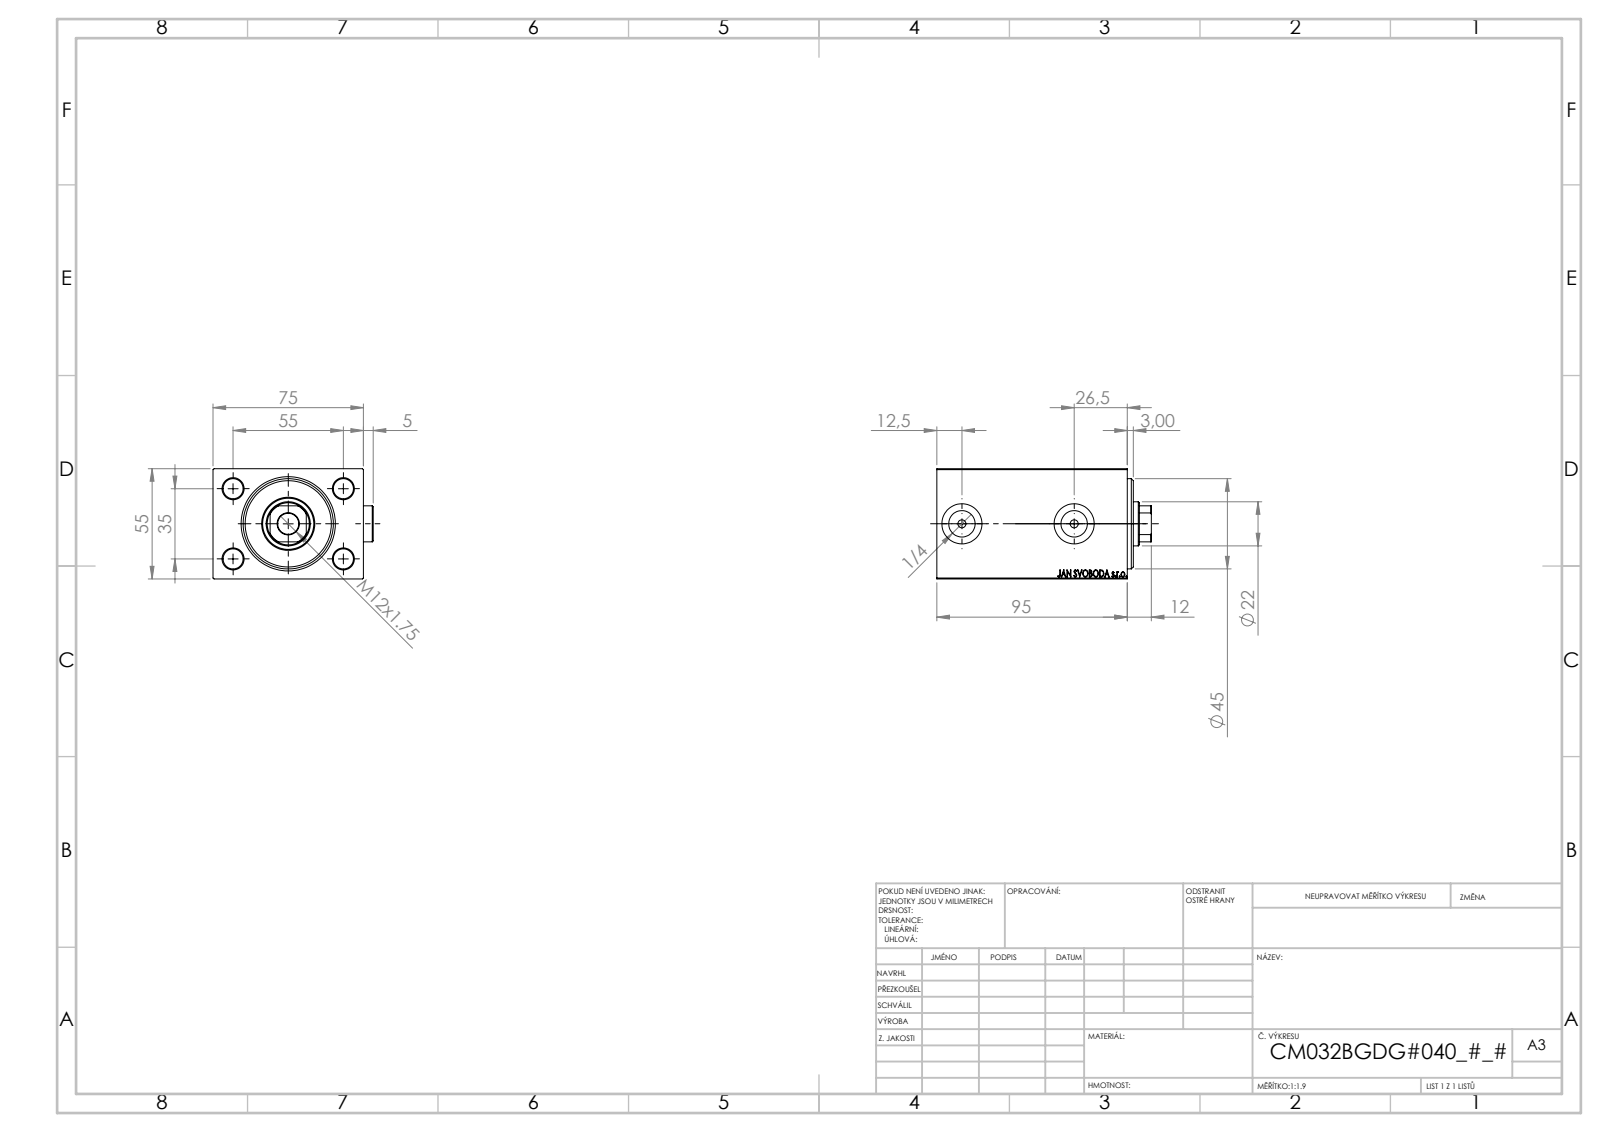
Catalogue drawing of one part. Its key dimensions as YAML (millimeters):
part_name: "Zatka_OIL_PORT; V450CM_VC_B; V450CM_B_Body; V450CM_B_VCP"
step_written_by: "SolidWorks 2019 (CONFIG_CONTROL_DESIGN)"
units: millimeters
bodies: {solids: 5, faces: 935, planar: 435, cylindrical: 70, other: 430}
overall_size: [107, 79.9, 55]
volume: 362108
surface_area: 66059
round_holes:
  - {diameter: 10, count: 4}
  - {diameter: 4, count: 2}
  - {diameter: 13.16, count: 2}
  - {diameter: 20, count: 2}
  - {diameter: 10.5, count: 1}
  - {diameter: 22, count: 1}
  - {diameter: 25.5, count: 1}
  - {diameter: 26.5, count: 1}
  - {diameter: 32, count: 1}
  - {diameter: 34, count: 1}
  - {diameter: 45, count: 1}
round_bosses_or_shafts:
  - {diameter: 18, count: 2}
partial_cylinders:
  - {radius: 10.5, count: 1}
face_to_face_distances: [55, 75, 95, 5, 85, 10, 80, 90, 74.9, 3]
hole_center_spacings: [32.6, 35, 55, 65.19, 56]
